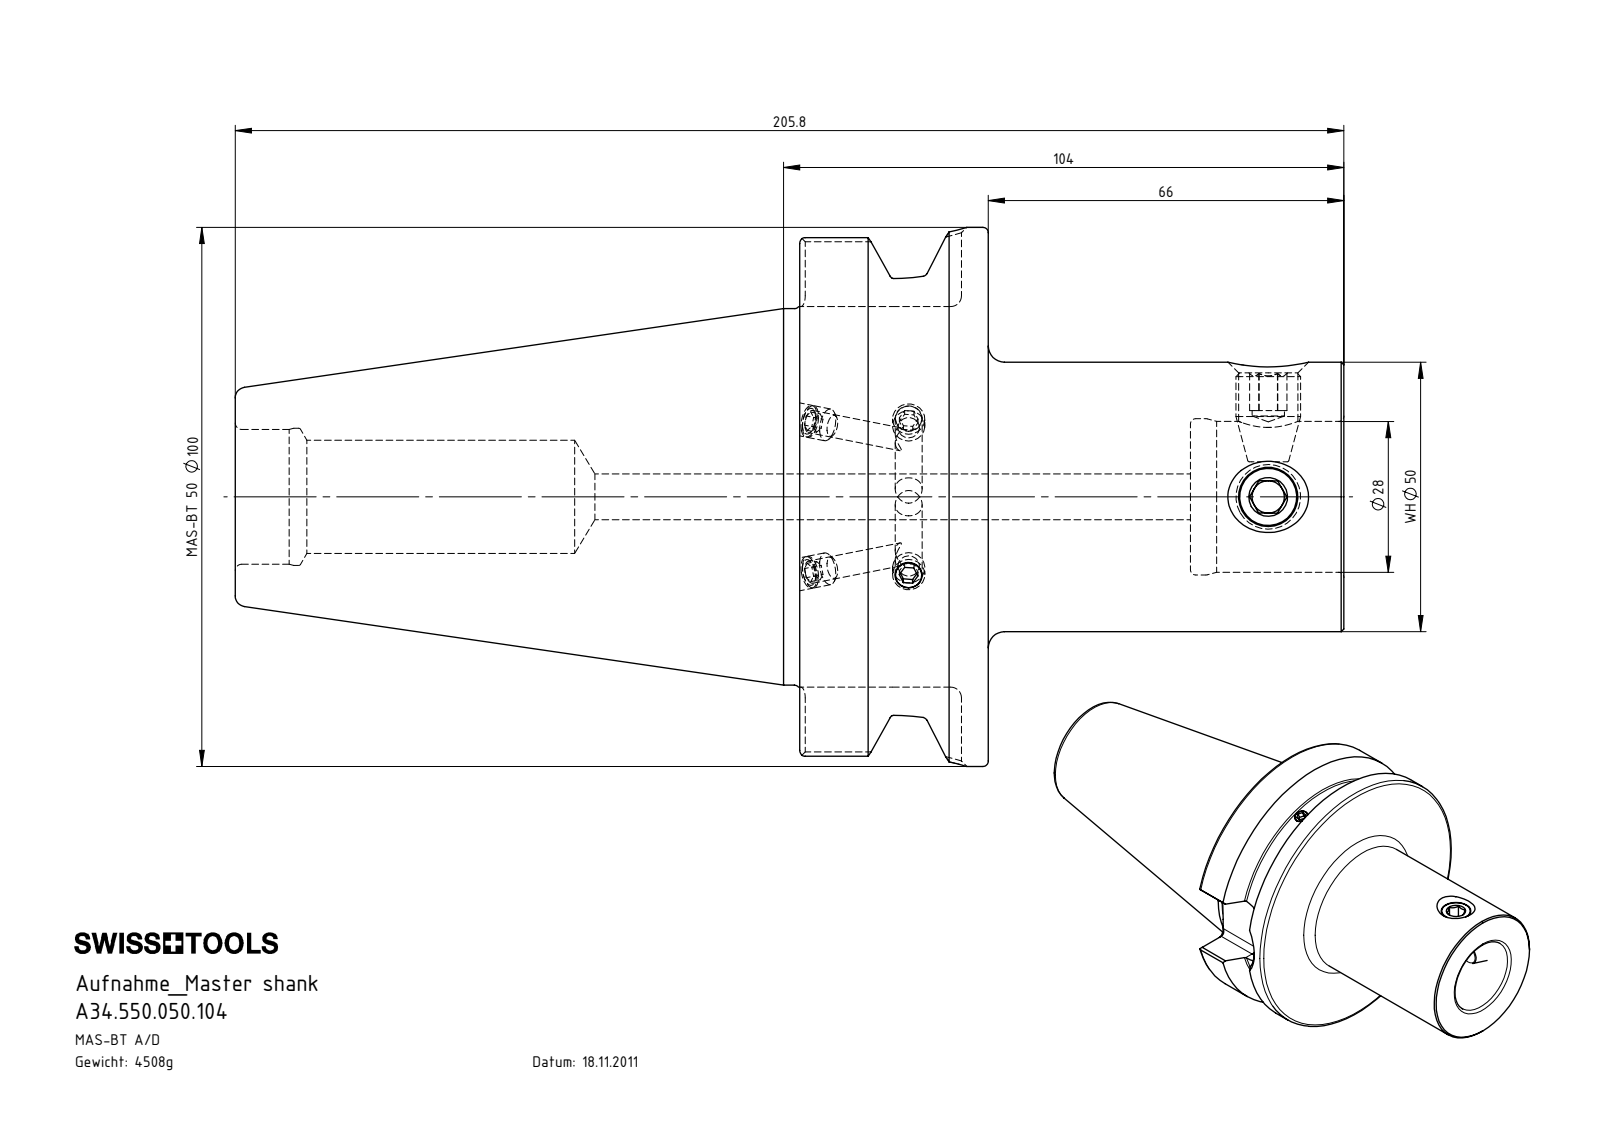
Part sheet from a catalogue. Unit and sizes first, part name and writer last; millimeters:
Units: millimetres
Overall size (bounding box): 205.8 × 100 × 100
Round holes (diameter × count): ⌀6 ×4, ⌀4.2 ×2, ⌀11 ×2, ⌀5 ×1, ⌀8.5 ×1, ⌀21 ×1, ⌀25 ×1, ⌀25.45 ×1, ⌀28 ×1, ⌀29 ×1
Round bosses / shafts (diameter × count): ⌀12 ×2, ⌀6 ×2, ⌀100 ×1, ⌀85 ×1, ⌀69.85 ×1, ⌀50 ×1
Partial cylindrical surfaces — rounded edges, fillets, slot ends (radius × count): R2 ×8, R12.85 ×1
Main face-to-face distances: 35, 101, 66, 70.6, 72.5, 37.5, 28.5, 104.8, 139.8, 177.3
Volume: 574 667 mm³ · Surface area: 68 480 mm²
Bodies: 7 solids, 240 faces (84 planar, 65 cylindrical, 91 other)
Part name (STEP PRODUCT): ISO 4026 - M6 x 5_PreviewCfg; WH5-ER1.001.017; A34.550.050.104; BB5-WH5.K01.104_C
STEP written by: SolidWorks 2017 (CONFIG_CONTROL_DESIGN)
